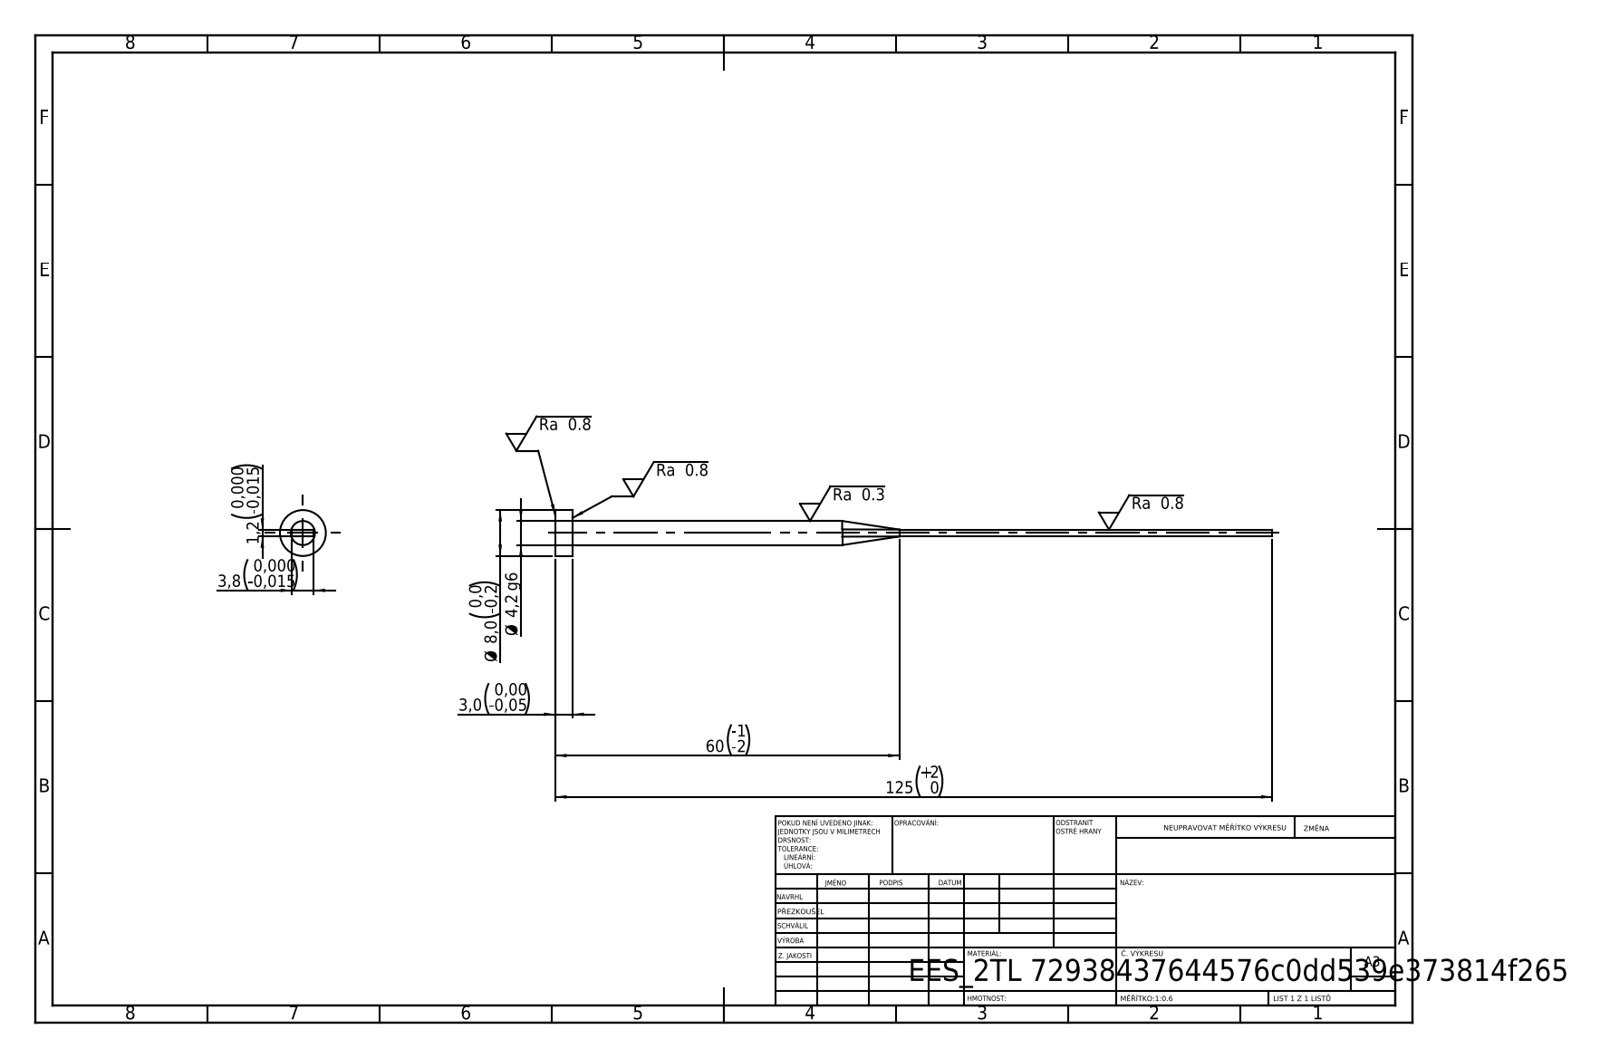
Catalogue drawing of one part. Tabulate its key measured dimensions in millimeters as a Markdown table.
| quantity | value |
| --- | --- |
| STEP written by | SolidWorks 2019 (CONFIG_CONTROL_DESIGN) |
| units | millimeters |
| bodies | 1 solid, 15 faces (7 planar, 4 cylindrical, 4 other) |
| overall size | 125 × 8 × 8 |
| volume | 1 187 mm³ |
| surface area | 1 549 mm² |
| round bosses / shafts (diameter × count) | 8 × 1, 4.2 × 1 |
| main face-to-face distances | 1.2, 3.8, 3, 125, 122 |
